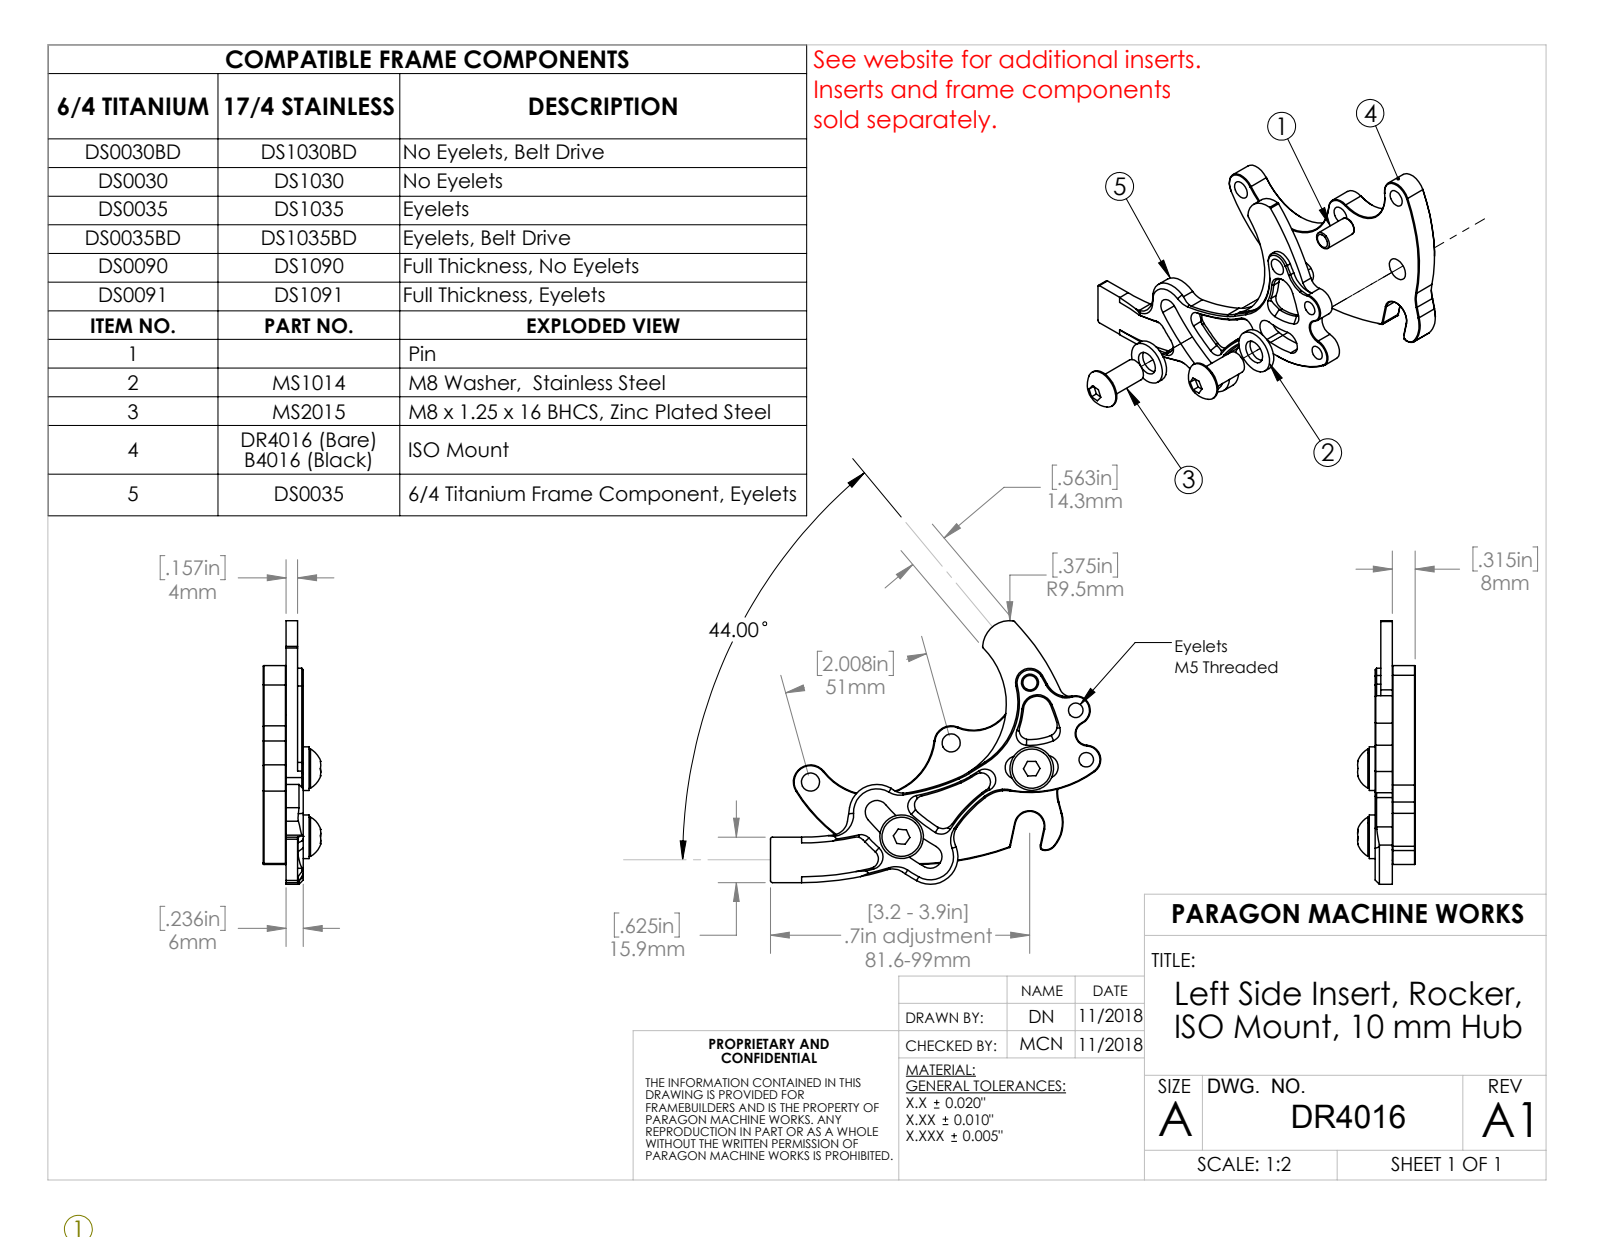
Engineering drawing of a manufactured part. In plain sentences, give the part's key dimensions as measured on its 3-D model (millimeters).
The part is named "DR4016". Its 3-D file was written by "SolidWorks 2018 (AUTOMOTIVE_DESIGN)". It is 1 solid with 121 faces: 15 planar, 56 cylindrical and 50 other. Overall it measures 96 by 65.4 by 8 millimeters. Its volume is 18 090 cubic millimeters and its surface area 10 660 square millimeters. Round holes: 2 of diameter 6.4, 1 of diameter 6, 1 of diameter 8, 1 of diameter 8. Partial cylindrical surfaces (rounded edges, fillets, slot ends): 8 of radius 0.3, 3 of radius 3.8, 3 of radius 6, 2 of radius 2.5, 2 of radius 12.7, 1 of radius 2.1, 1 of radius 3.4, 1 of radius 3.5. The main face-to-face distances are 8, 3.4, 4.6, 2.5, 10.2. The hole center spacings are 29.5, 30, 34.6, 37, 37.1, 51, 51.3, 70.
